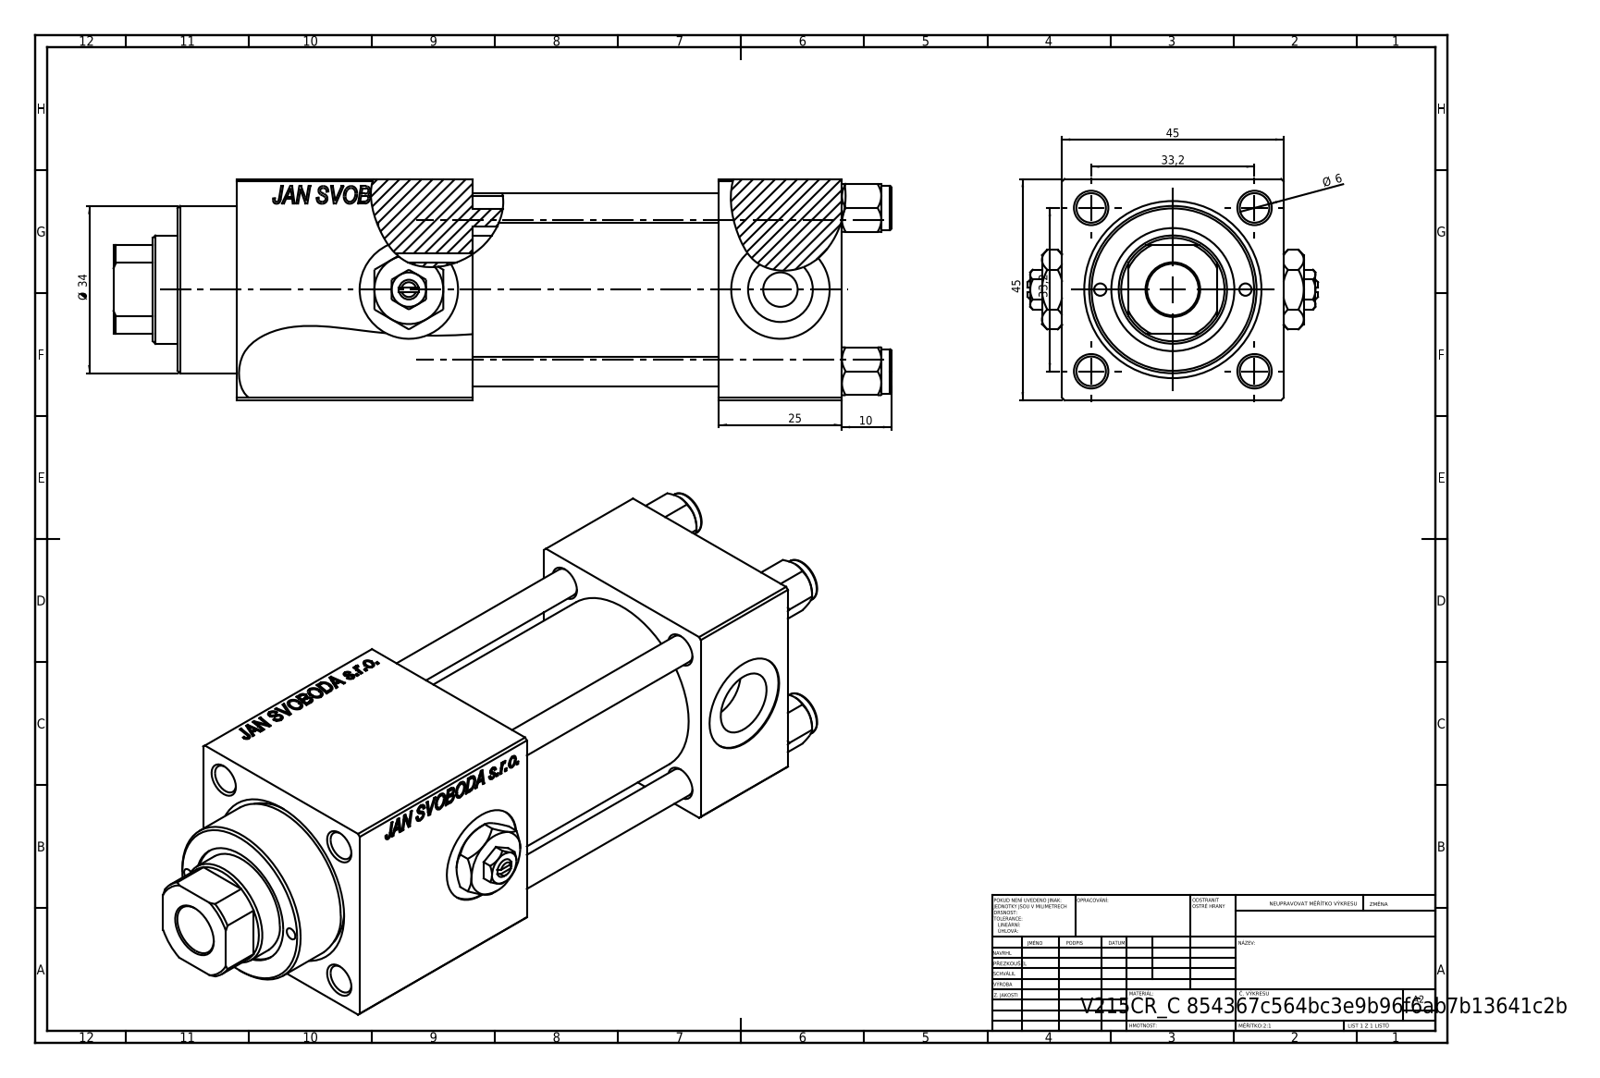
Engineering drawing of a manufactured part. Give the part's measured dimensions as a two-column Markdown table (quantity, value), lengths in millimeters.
| quantity | value |
| --- | --- |
| part name | V215CR_VCP_C; V215_VC_A; Zatka_pro_OIL_PORT; NUT_M5_C (+2 more) |
| STEP written by | SolidWorks 2019 (CONFIG_CONTROL_DESIGN) |
| units | millimeters |
| bodies | 13 solids, 1254 faces (574 planar, 102 cylindrical, 578 other) |
| overall size | 158 × 59 × 45 |
| volume | 208 138 mm³ |
| surface area | 73 410 mm² |
| round holes (diameter × count) | 6 × 4, 2.5 × 2, 7 × 2, 13.16 × 2, 20 × 2, 10.5 × 1, 22 × 1, 24 × 1, 25 × 1, 32 × 1, 33 × 1 |
| round bosses / shafts (diameter × count) | 9 × 4, 38 × 1, 34 × 1 |
| partial cylindrical surfaces (radius × count) | 10.5 × 1 |
| main face-to-face distances | 45, 25, 50, 123, 75, 98, 44.8, 48, 94.3, 69.3 |
| hole center spacings | 16.7, 23.48, 33.2, 35.47, 14.75, 46.95, 29.5, 75.5 |
